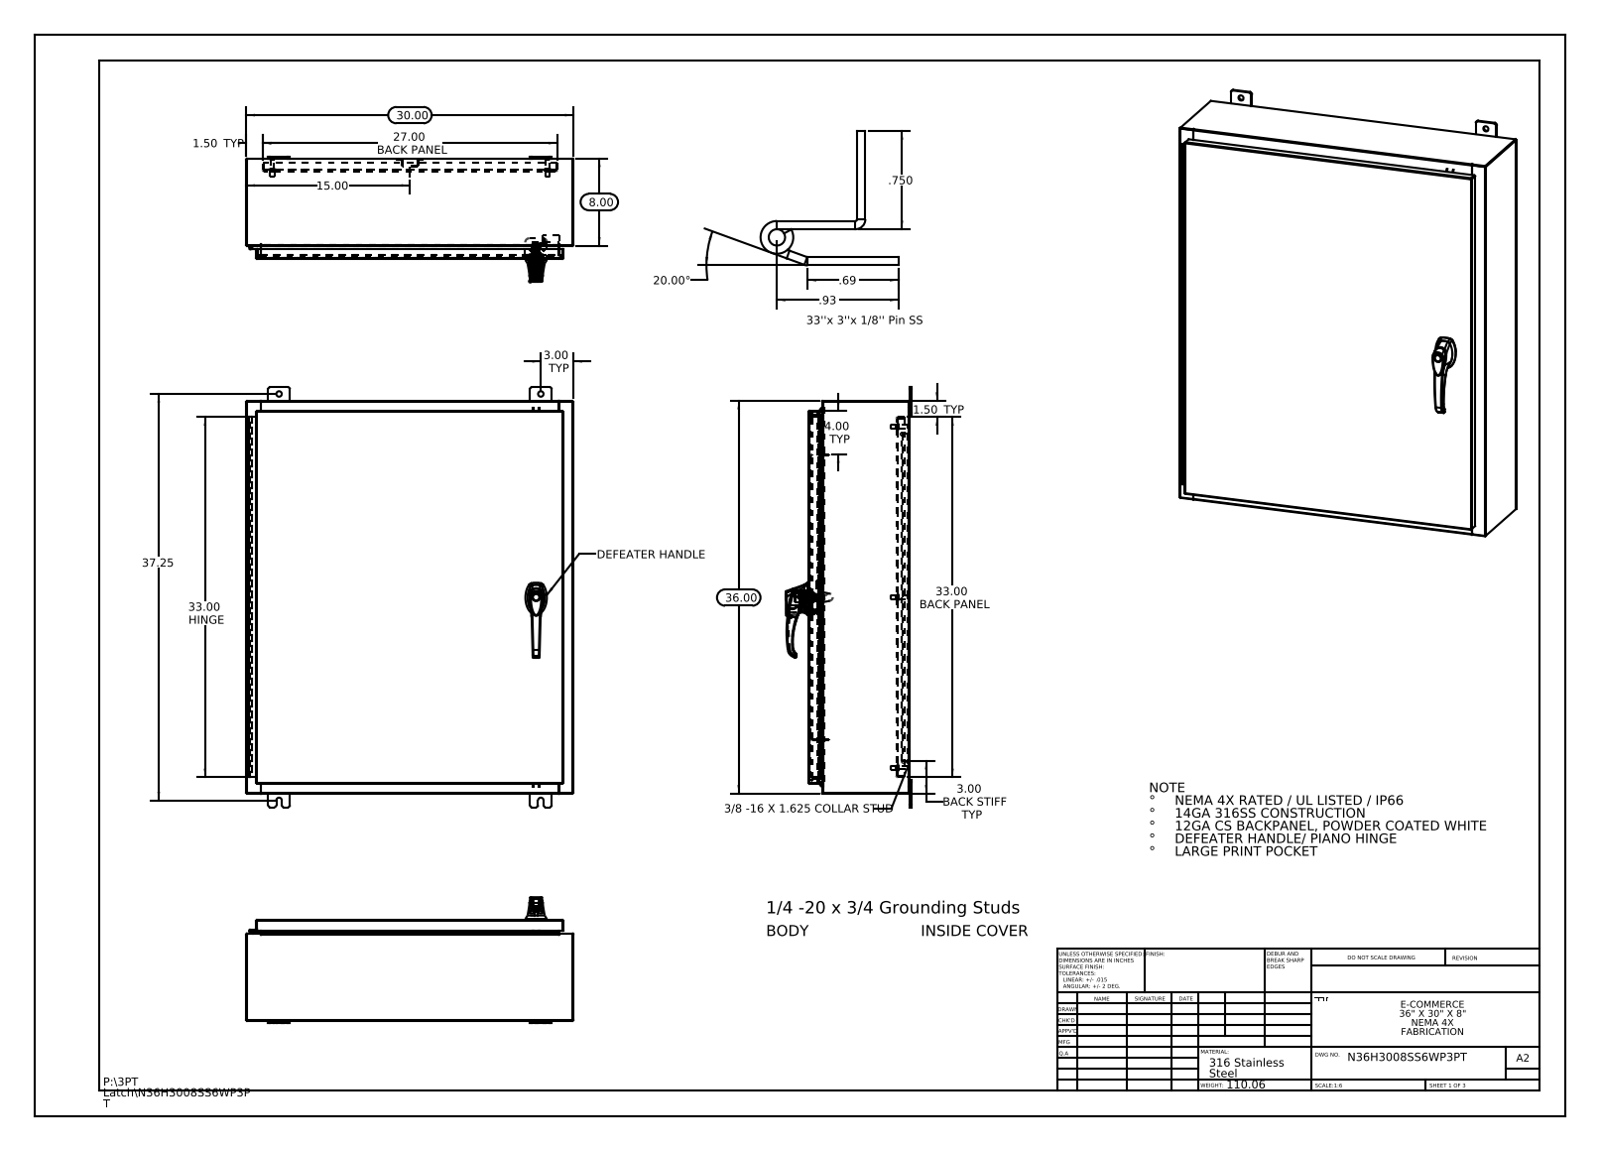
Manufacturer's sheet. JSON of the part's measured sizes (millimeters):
{"part_name": "N36H3008SS6WP3PT Body; 00005090; 21130102; N36H3008SS6WP3PT Cover (+8 more)", "step_written_by": "SolidWorks 2013 (CONFIG_CONTROL_DESIGN)", "units": "millimeters", "bodies": {"solids": 34, "faces": 2808, "planar": 1065, "cylindrical": 1069, "other": 674}, "overall_size": [977.9, 762, 292], "volume_mm3": 6378000, "surface_area_mm2": 6195000, "round_holes": [[12.7, 10], [6.4, 4], [3.5, 3], [4.1, 3], [2, 2], [5.2, 2], [8, 2], [11.1, 2], [3.2, 1], [3.2, 1], [5, 1], [7, 1]], "round_bosses_or_shafts": [[15.9, 6], [9.5, 6], [8.4, 6], [30, 1], [19, 1], [17.3, 1], [16.8, 1], [16.2, 1]], "partial_cylinders_radius": [[3, 37], [0.2, 33], [0.3, 28], [4.8, 24], [2.2, 22], [1, 15], [0.7, 12], [0.2, 6]], "face_to_face_distances": [1.9, 231.8, 229.9, 2.6, 233.7, 25.4, 206.4, 27.3, 204.5, 29.9], "hole_center_spacings": [288.6, 347.2, 396.9, 754.2, 641.4, 714.5, 7.5, 15.9]}
